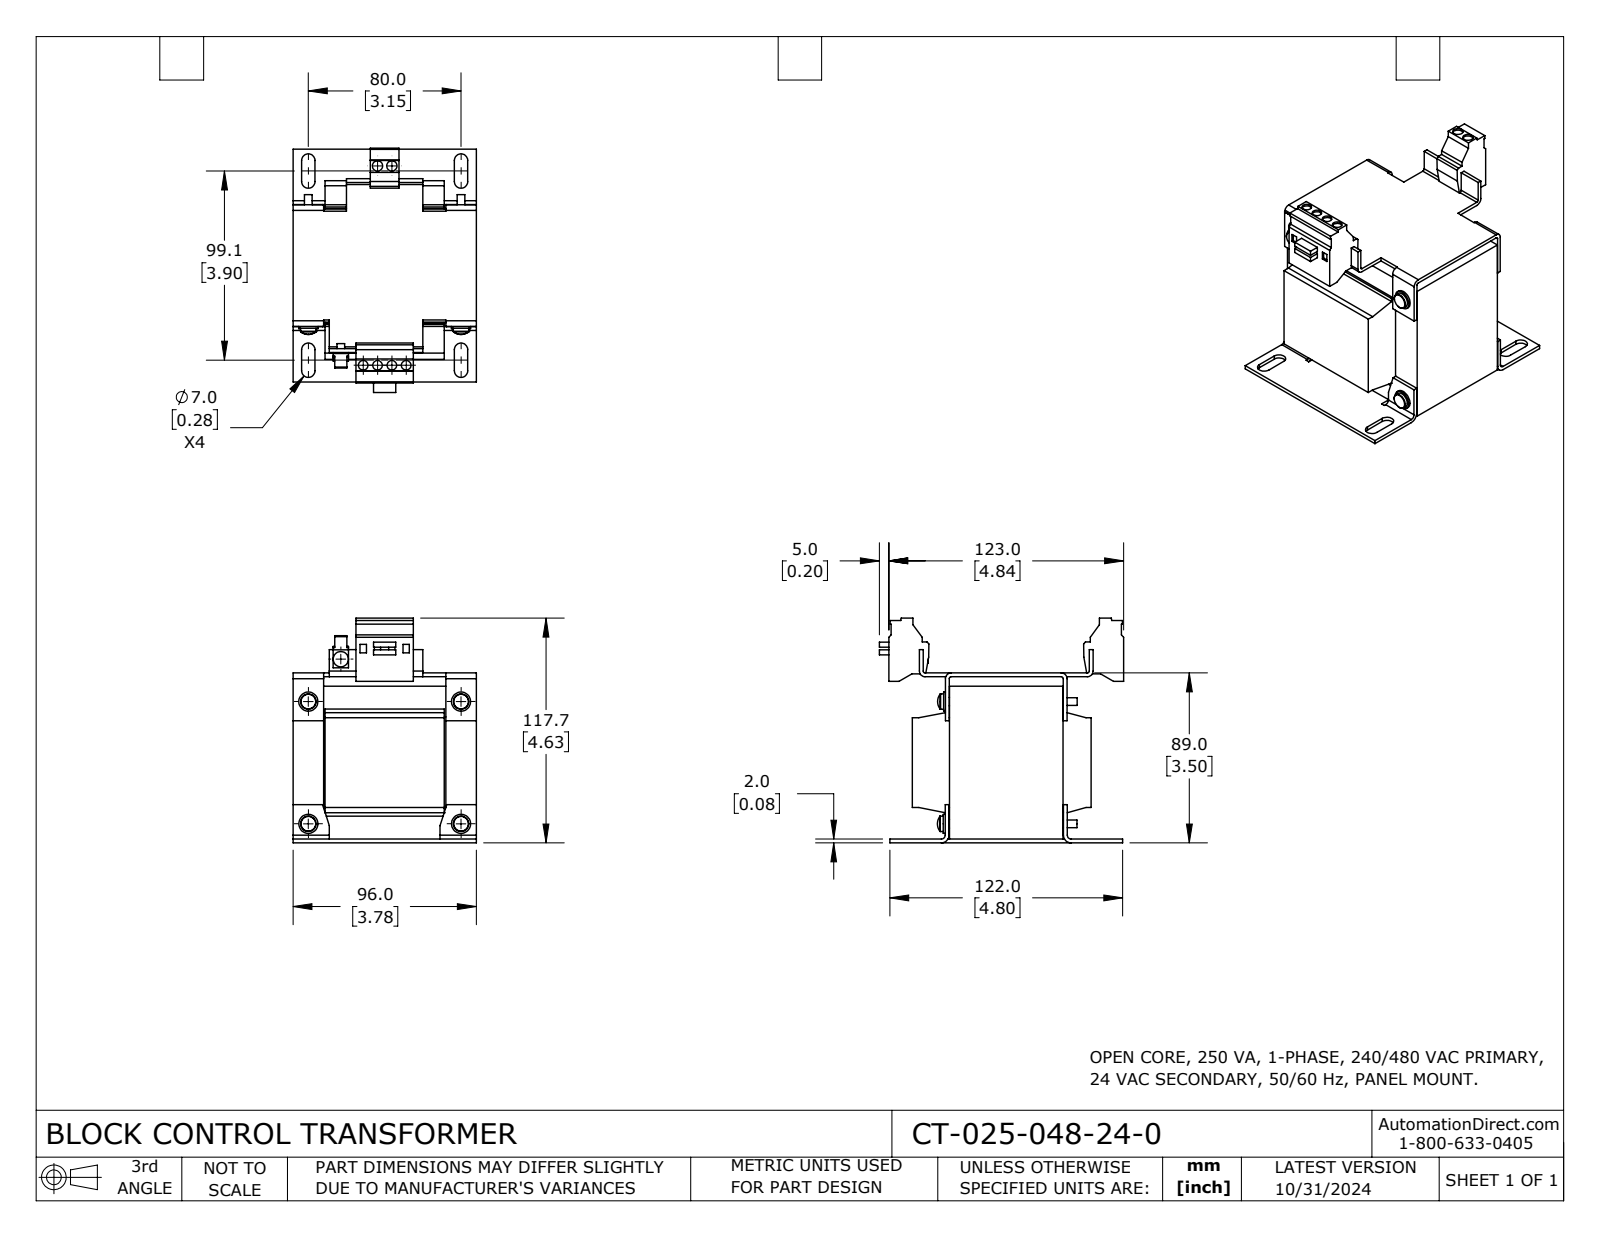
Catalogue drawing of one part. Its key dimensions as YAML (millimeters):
part_name: "CT-025-048-24-0"
step_written_by: "SolidWorks 2023 (CONFIG_CONTROL_DESIGN)"
units: millimeters
bodies: {solids: 1, faces: 337, planar: 237, cylindrical: 88, other: 12}
overall_size: [128, 117.7, 96]
volume: 620400
surface_area: 105900
round_holes:
  - {diameter: 5, count: 4}
  - {diameter: 5.4, count: 2}
round_bosses_or_shafts:
  - {diameter: 8, count: 5}
  - {diameter: 4, count: 5}
  - {diameter: 10, count: 4}
  - {diameter: 4.5, count: 4}
partial_cylinders:
  - {radius: 3.5, count: 8}
  - {radius: 1, count: 4}
  - {radius: 3, count: 4}
  - {radius: 2, count: 2}
  - {radius: 4, count: 2}
face_to_face_distances: [2, 87, 80, 16, 16.8, 79.2, 64, 89, 85, 5]
hole_center_spacings: [7.5, 104.7, 15, 104.4, 105.5, 22.5]
